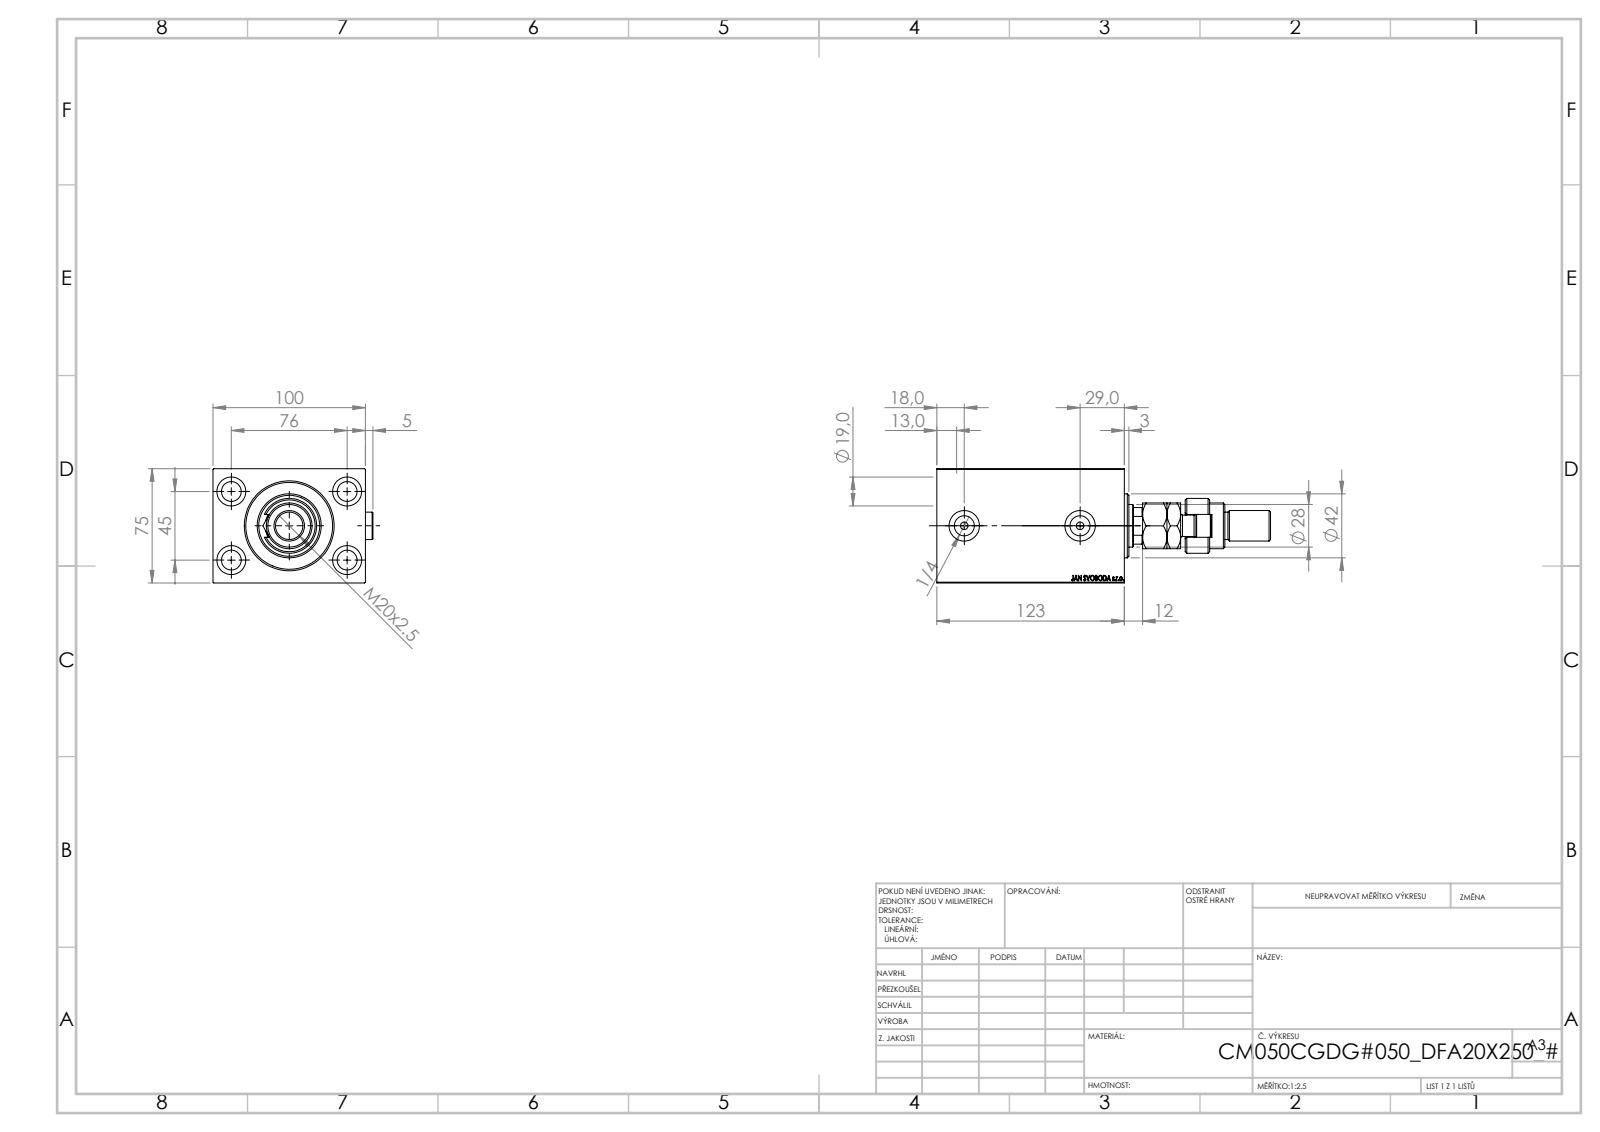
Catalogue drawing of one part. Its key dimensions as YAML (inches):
part_name: "V450CM_C_Body; FEMALE_PART_FOR_DFA; V450CM_VC_B; Zatka_OIL_PORT (+2 more)"
step_written_by: "SolidWorks 2019 (CONFIG_CONTROL_DESIGN)"
units: inches
bodies: {solids: 7, faces: 1004, planar: 471, cylindrical: 91, other: 442}
overall_size: [8.622, 4.13, 2.953]
volume: 49.96
surface_area: 218.1
round_holes:
  - {diameter: 0.512, count: 4}
  - {diameter: 0.748, count: 4}
  - {diameter: 0.197, count: 2}
  - {diameter: 0.518, count: 2}
  - {diameter: 0.787, count: 2}
  - {diameter: 0.728, count: 1}
  - {diameter: 1.102, count: 1}
  - {diameter: 1.24, count: 1}
  - {diameter: 1.969, count: 1}
  - {diameter: 2.047, count: 1}
  - {diameter: 2.244, count: 1}
round_bosses_or_shafts:
  - {diameter: 0.709, count: 3}
  - {diameter: 1.654, count: 1}
  - {diameter: 1.417, count: 1}
  - {diameter: 1.181, count: 1}
  - {diameter: 0.866, count: 1}
  - {diameter: 0.787, count: 1}
  - {diameter: 0.551, count: 1}
partial_cylinders:
  - {radius: 0.295, count: 1}
  - {radius: 0.472, count: 1}
  - {radius: 0.531, count: 1}
face_to_face_distances: [2.953, 3.937, 4.843, 4.291, 0.551, 0.472, 3.819, 1.969, 2.441, 1.181]
hole_center_spacings: [1.739, 2.992, 1.772, 3.477]
